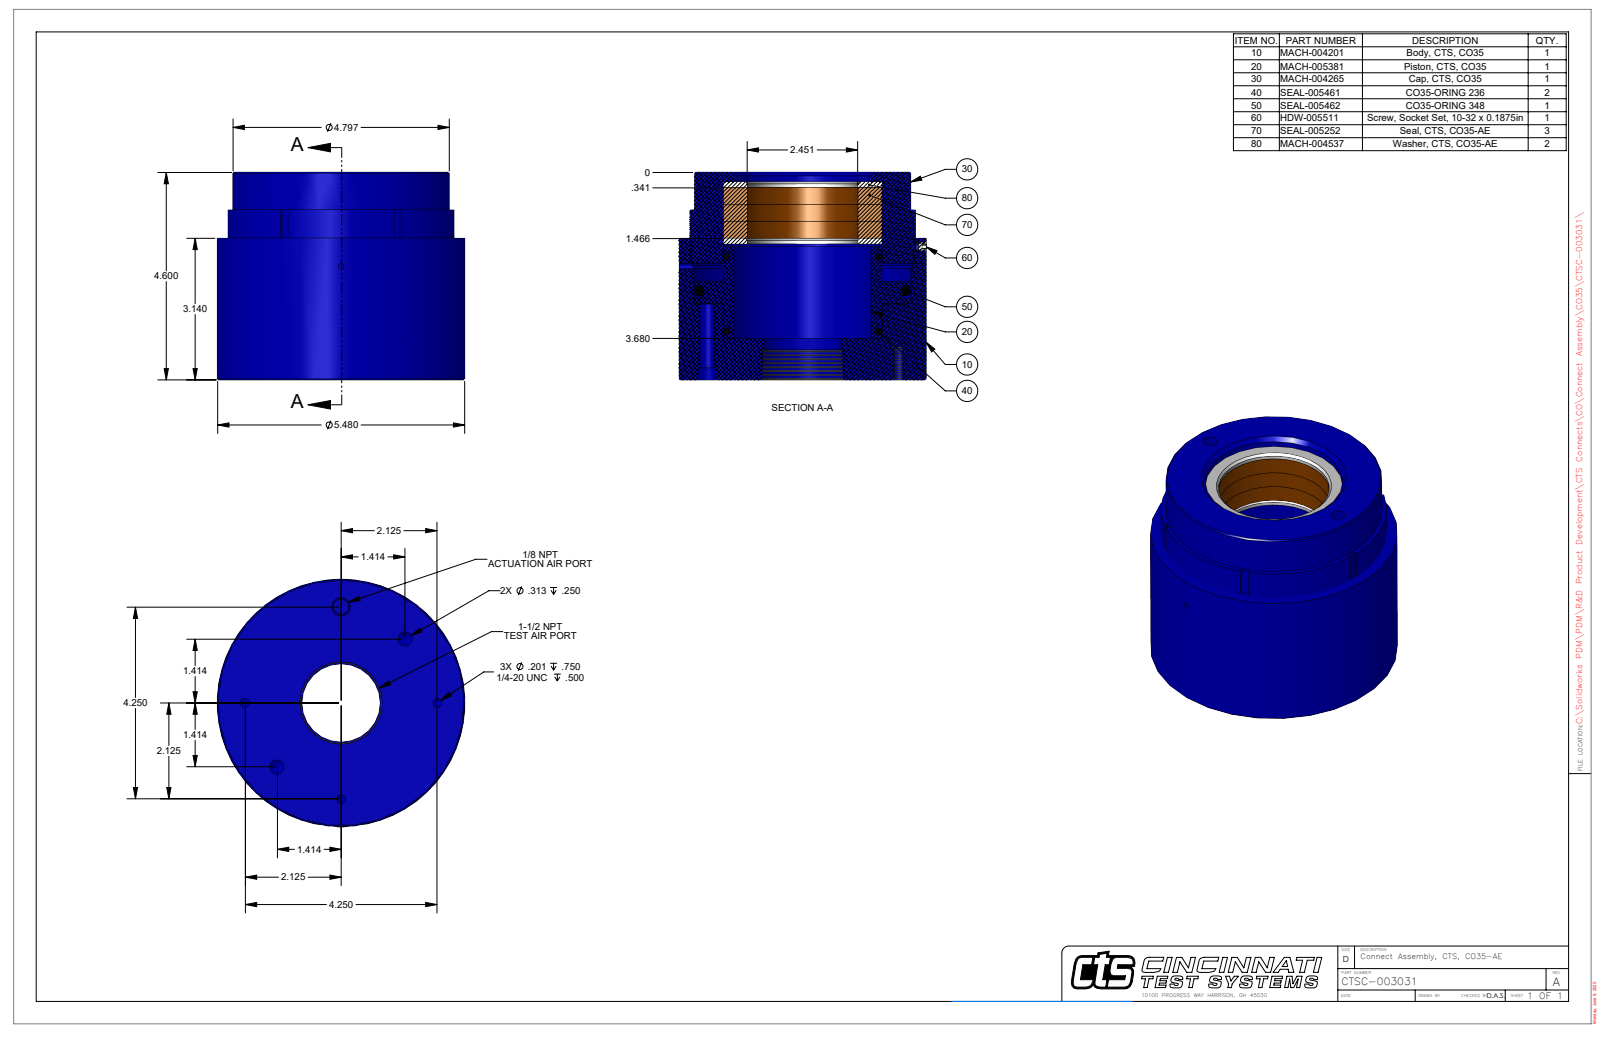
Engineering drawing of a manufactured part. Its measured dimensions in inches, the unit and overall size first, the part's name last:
Units: inches
Overall size (bounding box): 5.486 × 5.48 × 4.6
Round holes (diameter × count): ⌀0.313 ×4, ⌀0.201 ×3, ⌀0.125 ×1, ⌀0.332 ×1, ⌀1.719 ×1, ⌀2.451 ×1, ⌀2.453 ×1, ⌀3.05 ×1, ⌀3.1 ×1, ⌀3.517 ×1
Round bosses / shafts (diameter × count): ⌀5.48 ×1, ⌀5 ×1, ⌀4.797 ×1, ⌀3.513 ×1, ⌀3.509 ×1
Partial cylindrical surfaces — rounded edges, fillets, slot ends (radius × count): R2.46 ×1, R2.724 ×1
Main face-to-face distances: 4.259, 4.6, 0.341, 0.125, 4.384, 0.216, 0.92, 3.339, 3.464, 3.68
Hole centre spacings: 1.583, 2, 2.125, 2.918, 3.005, 3.811, 0.125, 1.531
Volume: 75.44 in³ · Surface area: 183 in²
Bodies: 2 solids, 132 faces (50 planar, 58 cylindrical, 24 other)
Part name (STEP PRODUCT): CTSC-003031
STEP written by: SolidWorks 2023 (AUTOMOTIVE_DESIGN)
